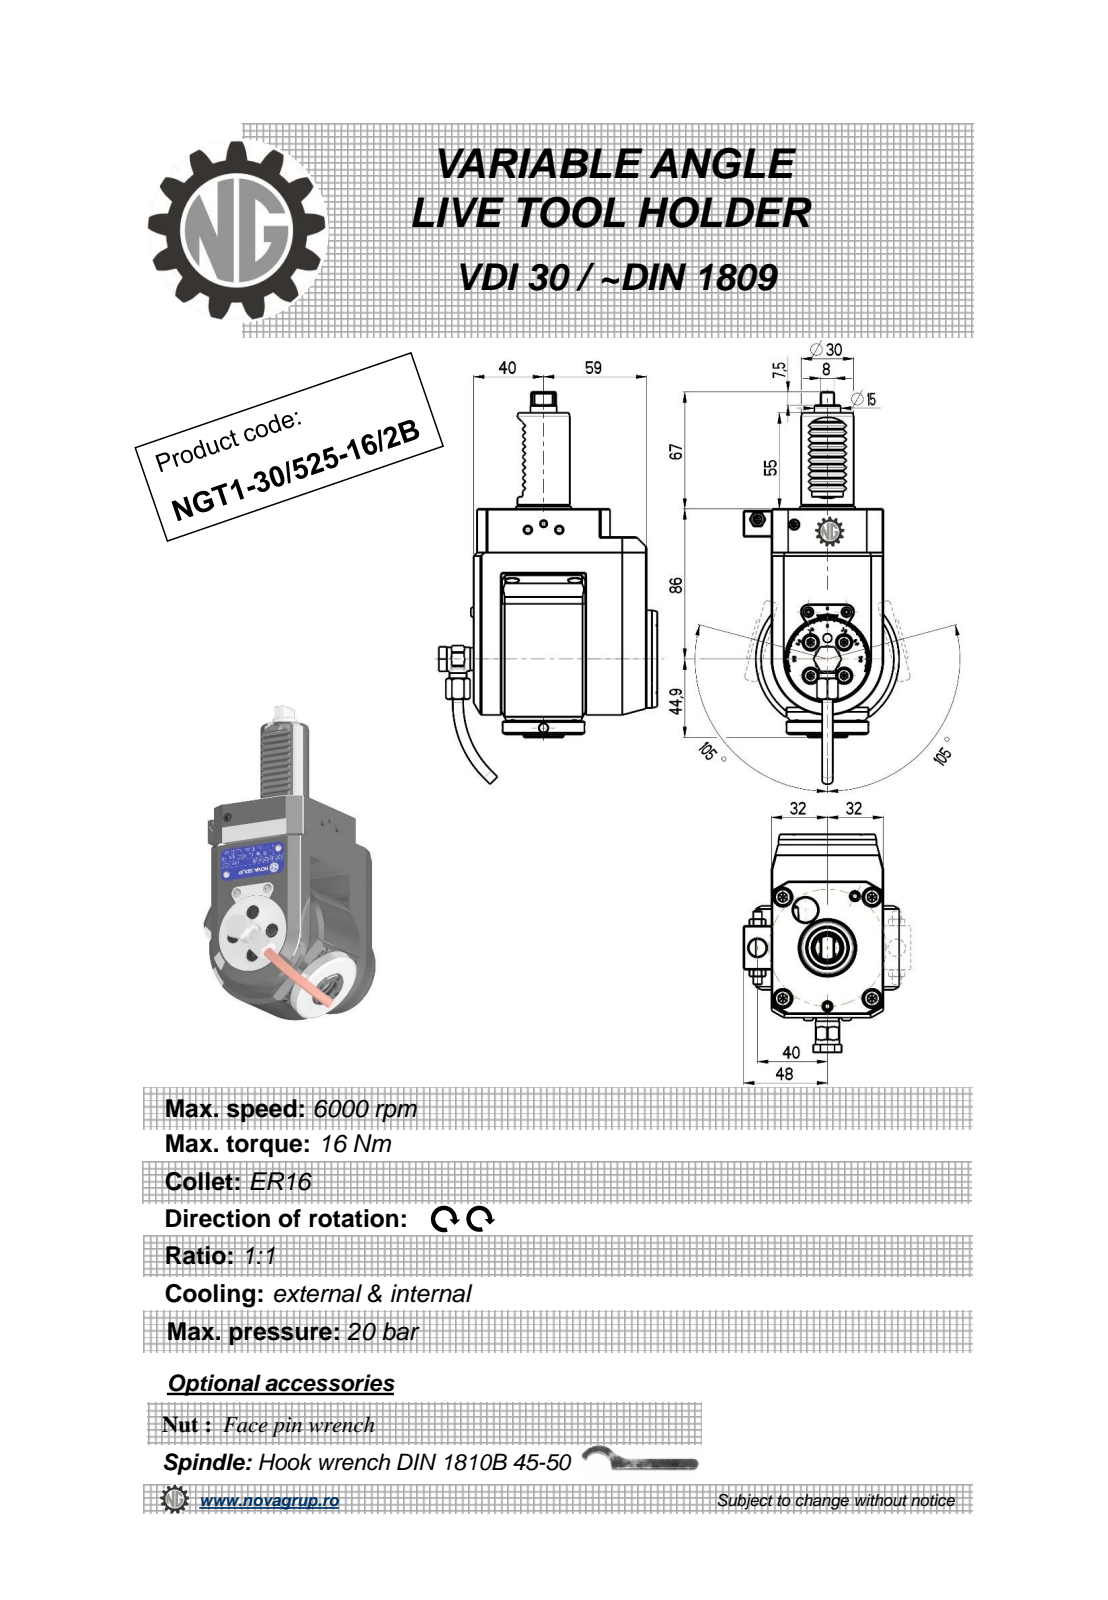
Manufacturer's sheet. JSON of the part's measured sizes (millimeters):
{"part_name": "NGT1_30_521_16_2B", "step_written_by": "PRO/ENGINEER BY PARAMETRIC TECHNOLOGY CORPORATION, 2010280 (CONFIG_CONTROL_DESIGN)", "units": "millimeters", "bodies": {"solids": 1, "faces": 510, "planar": 218, "cylindrical": 140, "other": 152}, "overall_size": [224.67, 124.9, 89], "volume_mm3": 776914, "surface_area_mm2": 71467, "round_holes": [[3.2, 4], [4, 3], [5, 2], [3, 1], [4.2, 1], [6.2, 1], [9, 1], [9.5, 1], [10, 1], [11, 1], [12.5, 1]], "round_bosses_or_shafts": [[10, 2], [6, 2], [5.7, 2], [56, 1], [47, 1], [35, 1], [30, 1], [23, 1]], "partial_cylinders_radius": [[0.26, 12], [0.3, 10], [0.16, 6], [0.5, 4], [0.8, 2], [1, 2], [7.2, 1], [7.7, 1]], "face_to_face_distances": [64, 16, 37, 99, 6, 105, 21, 14, 62, 83], "hole_center_spacings": [9.25, 13.08, 18.5, 41.06, 49.87, 50.26, 0.4, 30.75]}
